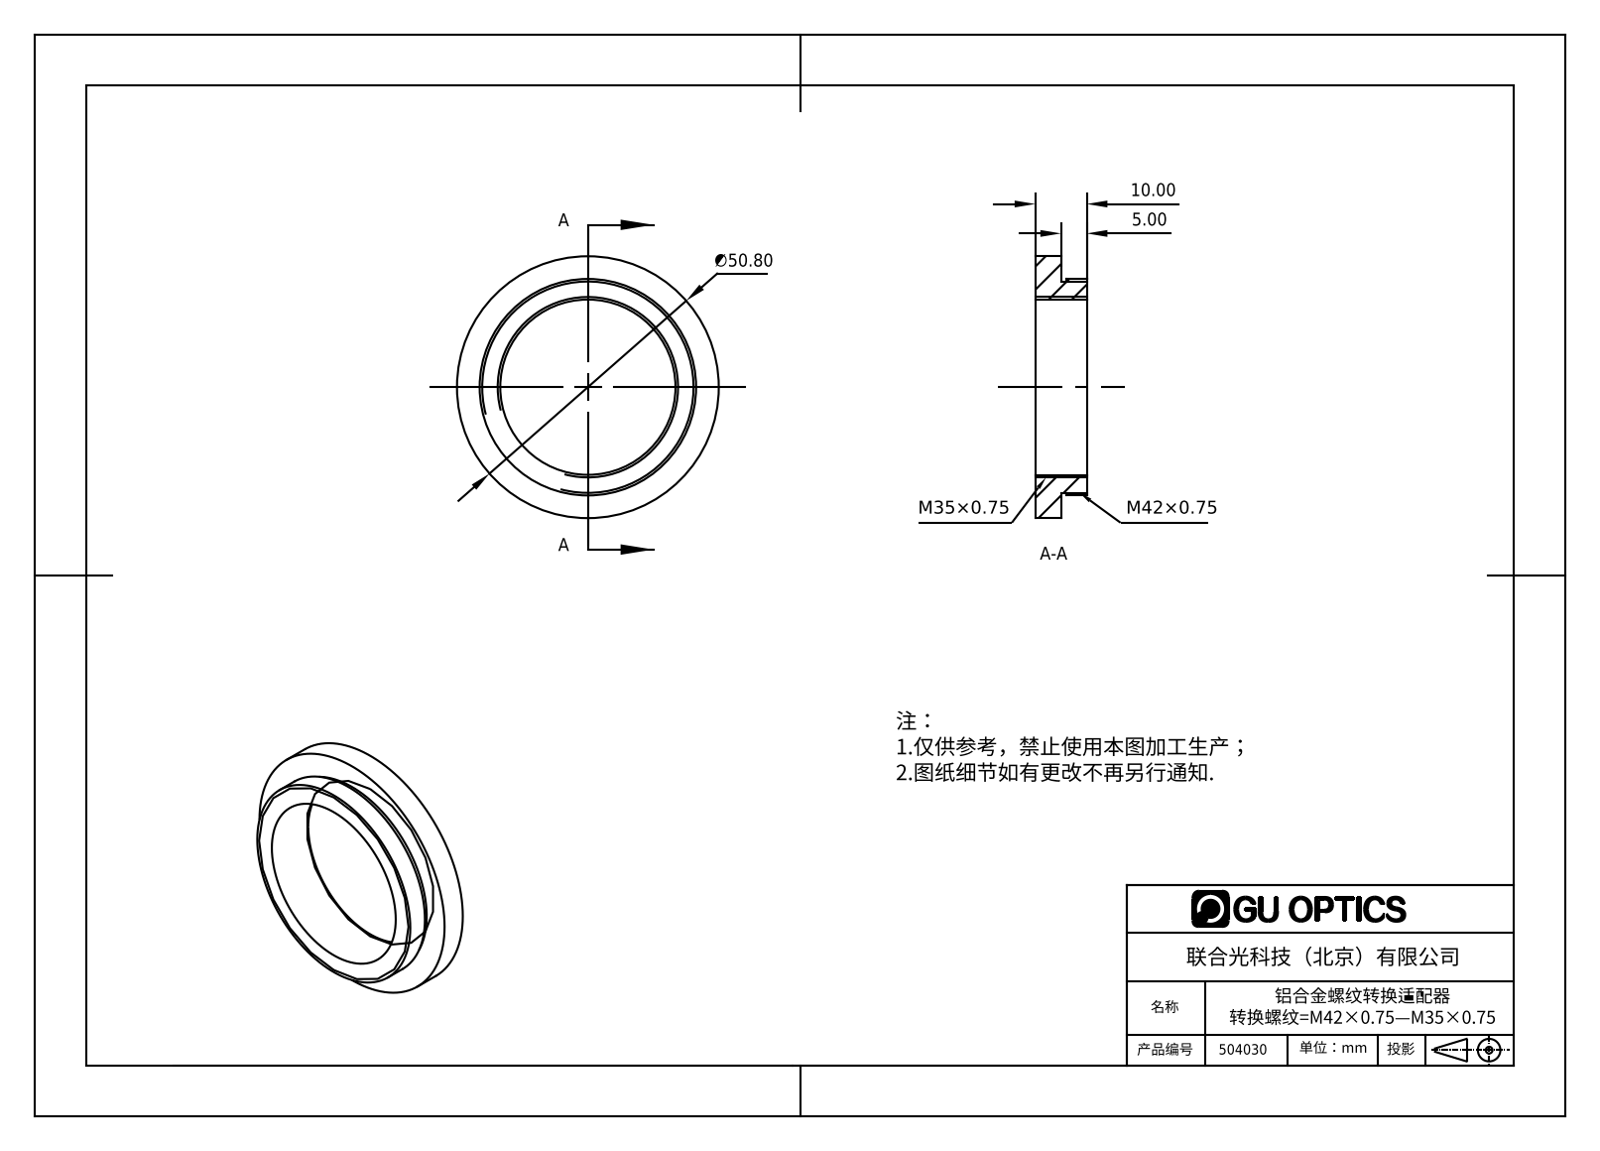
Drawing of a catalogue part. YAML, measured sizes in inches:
part_name: "504030"
step_written_by: "SolidWorks 2016 (AUTOMOTIVE_DESIGN)"
units: inches
bodies: {solids: 1, faces: 12, planar: 4, cylindrical: 8, other: 0}
overall_size: [2, 2, 0.394]
volume: 0.483
surface_area: 7.581
round_holes:
  - {diameter: 1.339, count: 1}
round_bosses_or_shafts:
  - {diameter: 2, count: 1}
  - {diameter: 1.654, count: 1}
  - {diameter: 1.614, count: 1}
face_to_face_distances: [0.197, 0.394, 0.236, 0.039, 0.157]
